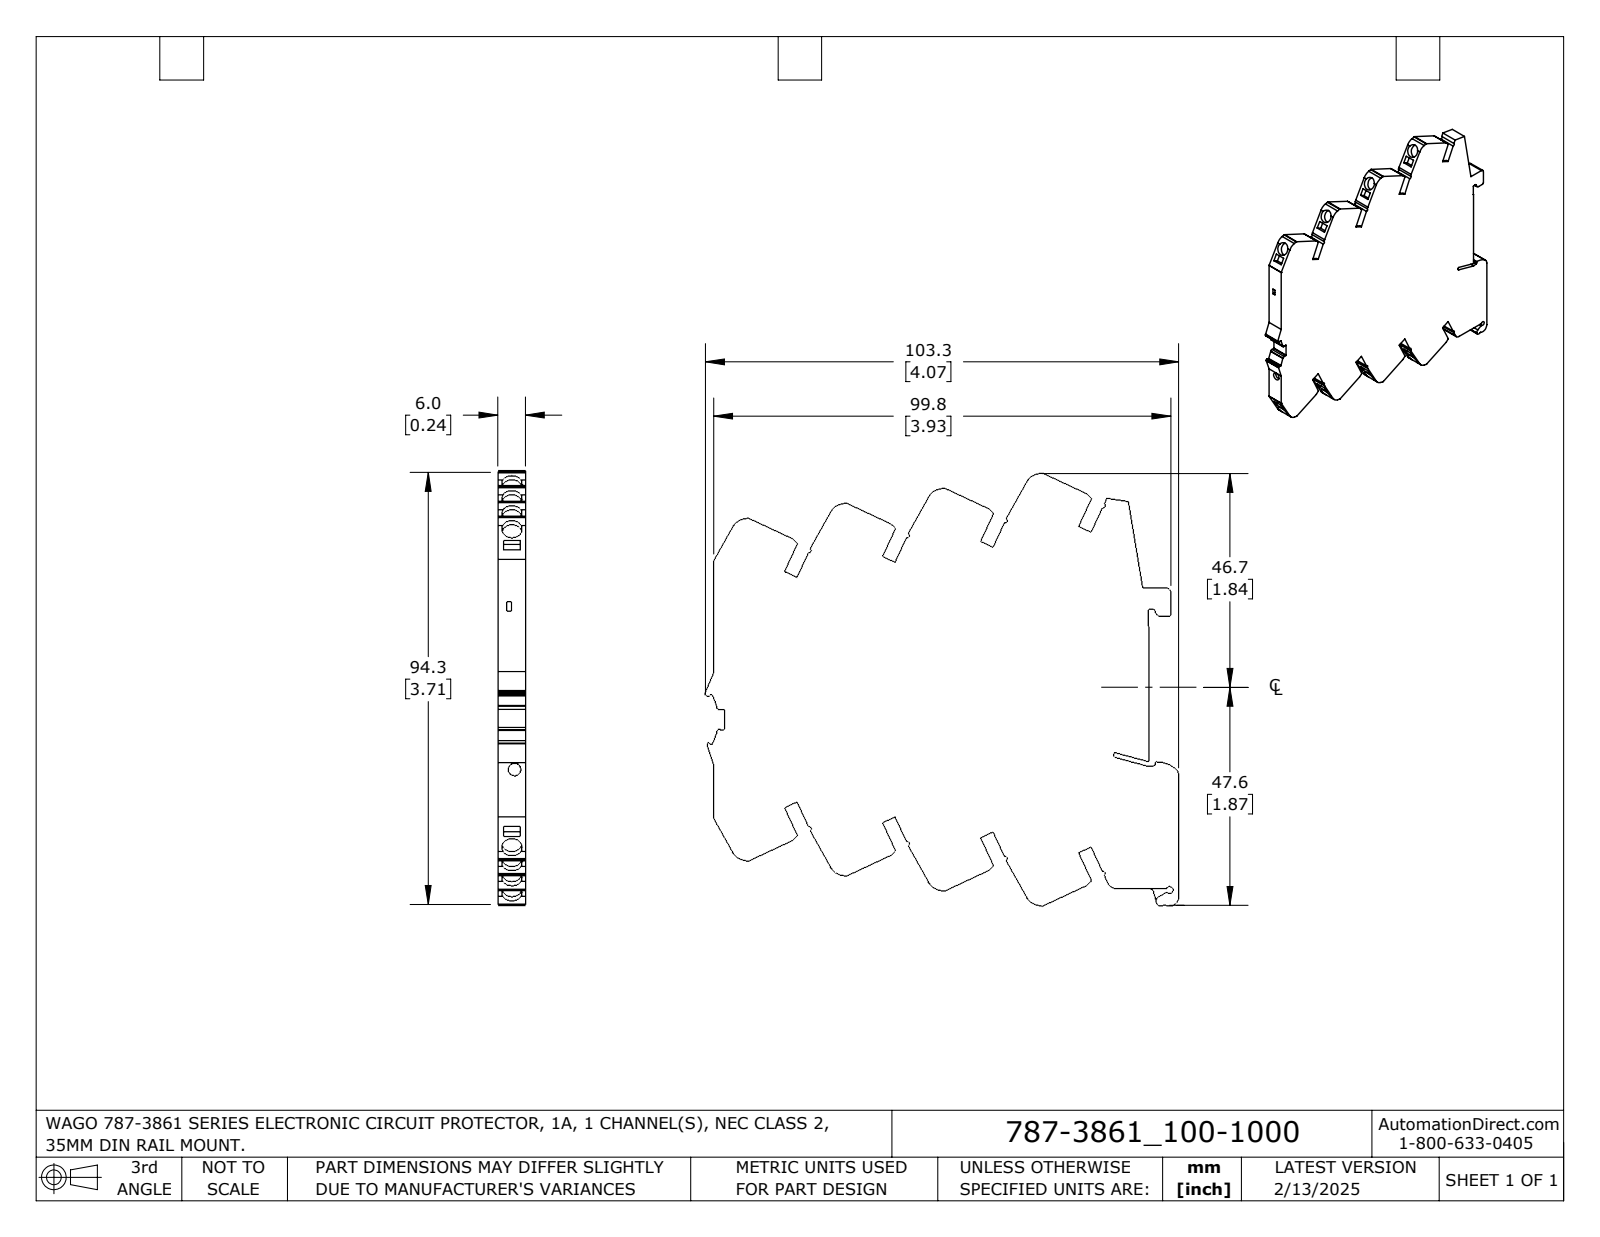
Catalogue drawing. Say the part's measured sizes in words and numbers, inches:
The part is named "787-3861_100-1000_HI". Its 3-D file was written by "SolidWorks 2024 (AUTOMOTIVE_DESIGN)". It is 1 solid with 262 faces: 197 planar, 65 cylindrical and 0 other. Overall it measures 4.067 by 3.711 by 0.236 inches. Its volume is 2.685 cubic inches and its surface area 29.24 square inches. Round holes: 8 of diameter 0.173, 1 of diameter 0.106. Partial cylindrical surfaces (rounded edges, fillets, slot ends): 13 of radius 0.008, 12 of radius 0.02, 8 of radius 0.016, 8 of radius 0.132, 5 of radius 0.039, 3 of radius 0.012, 3 of radius 0.079, 2 of radius 0.018. The main face-to-face distances are 0.236, 0.708, 0.67, 0.473, 0.118, 1.417, 0.472, 0.945, 0.59, 1.34. The hole center spacings are 0.526, 0.525, 1.051, 1.052, 1.577.
